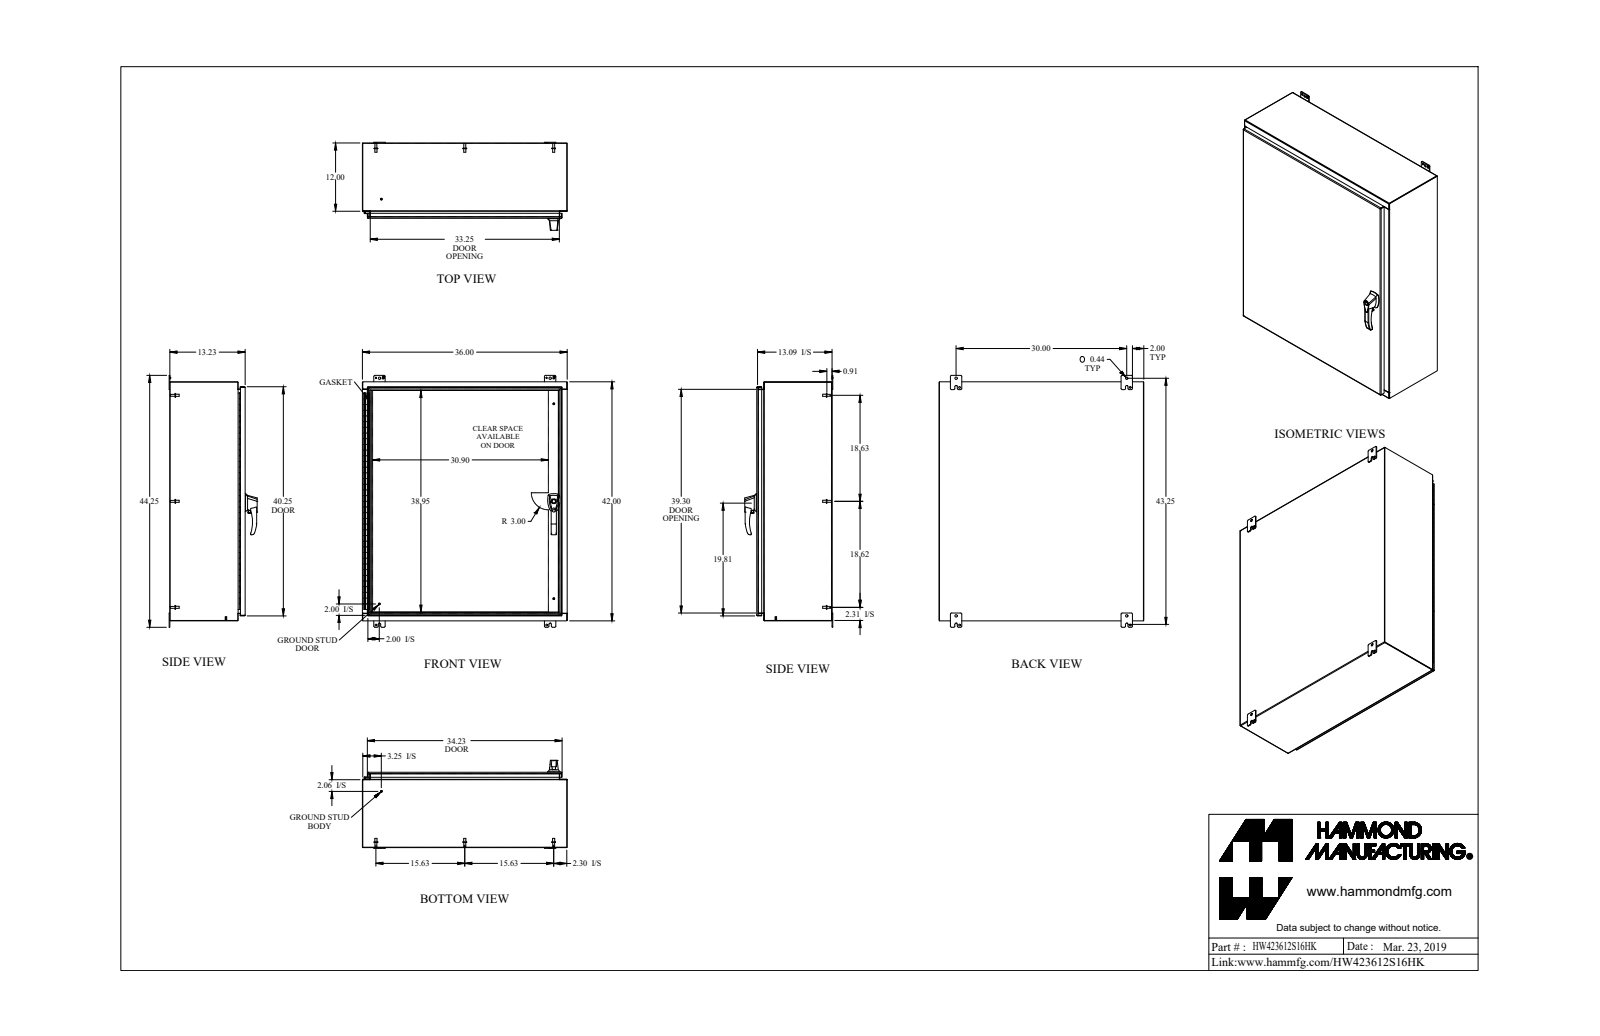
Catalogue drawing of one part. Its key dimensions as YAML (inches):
part_name: "HW423612S16HK"
step_written_by: "SolidWorks 2018 (AUTOMOTIVE_DESIGN)"
units: inches
bodies: {solids: 47, faces: 1529, planar: 715, cylindrical: 678, other: 136}
overall_size: [44.25, 36, 15.473]
volume: 456.1
surface_area: 11295
round_holes:
  - {diameter: 0.176, count: 6}
  - {diameter: 0.313, count: 4}
  - {diameter: 0.25, count: 3}
  - {diameter: 0.265, count: 3}
  - {diameter: 0.413, count: 3}
  - {diameter: 0.196, count: 2}
  - {diameter: 0.256, count: 2}
  - {diameter: 0.394, count: 2}
  - {diameter: 0.437, count: 2}
  - {diameter: 0.11, count: 1}
  - {diameter: 0.233, count: 1}
  - {diameter: 0.33, count: 1}
round_bosses_or_shafts:
  - {diameter: 0.375, count: 13}
  - {diameter: 0.65, count: 8}
  - {diameter: 0.332, count: 8}
  - {diameter: 0.25, count: 7}
  - {diameter: 0.156, count: 6}
  - {diameter: 1, count: 3}
  - {diameter: 0.63, count: 2}
  - {diameter: 0.51, count: 2}
partial_cylinders:
  - {radius: 0.25, count: 27}
  - {radius: 0.188, count: 23}
  - {radius: 0.036, count: 14}
  - {radius: 0.108, count: 14}
  - {radius: 0.06, count: 12}
  - {radius: 0.125, count: 9}
  - {radius: 0.218, count: 8}
  - {radius: 0.03, count: 6}
face_to_face_distances: [0.072, 13.138, 13.066, 0.095, 13.233, 13.161, 35.928, 41.928, 35.856, 36]
hole_center_spacings: [17.118, 17.119, 34.237, 1.11, 1.111, 17.119, 30, 43.38]
